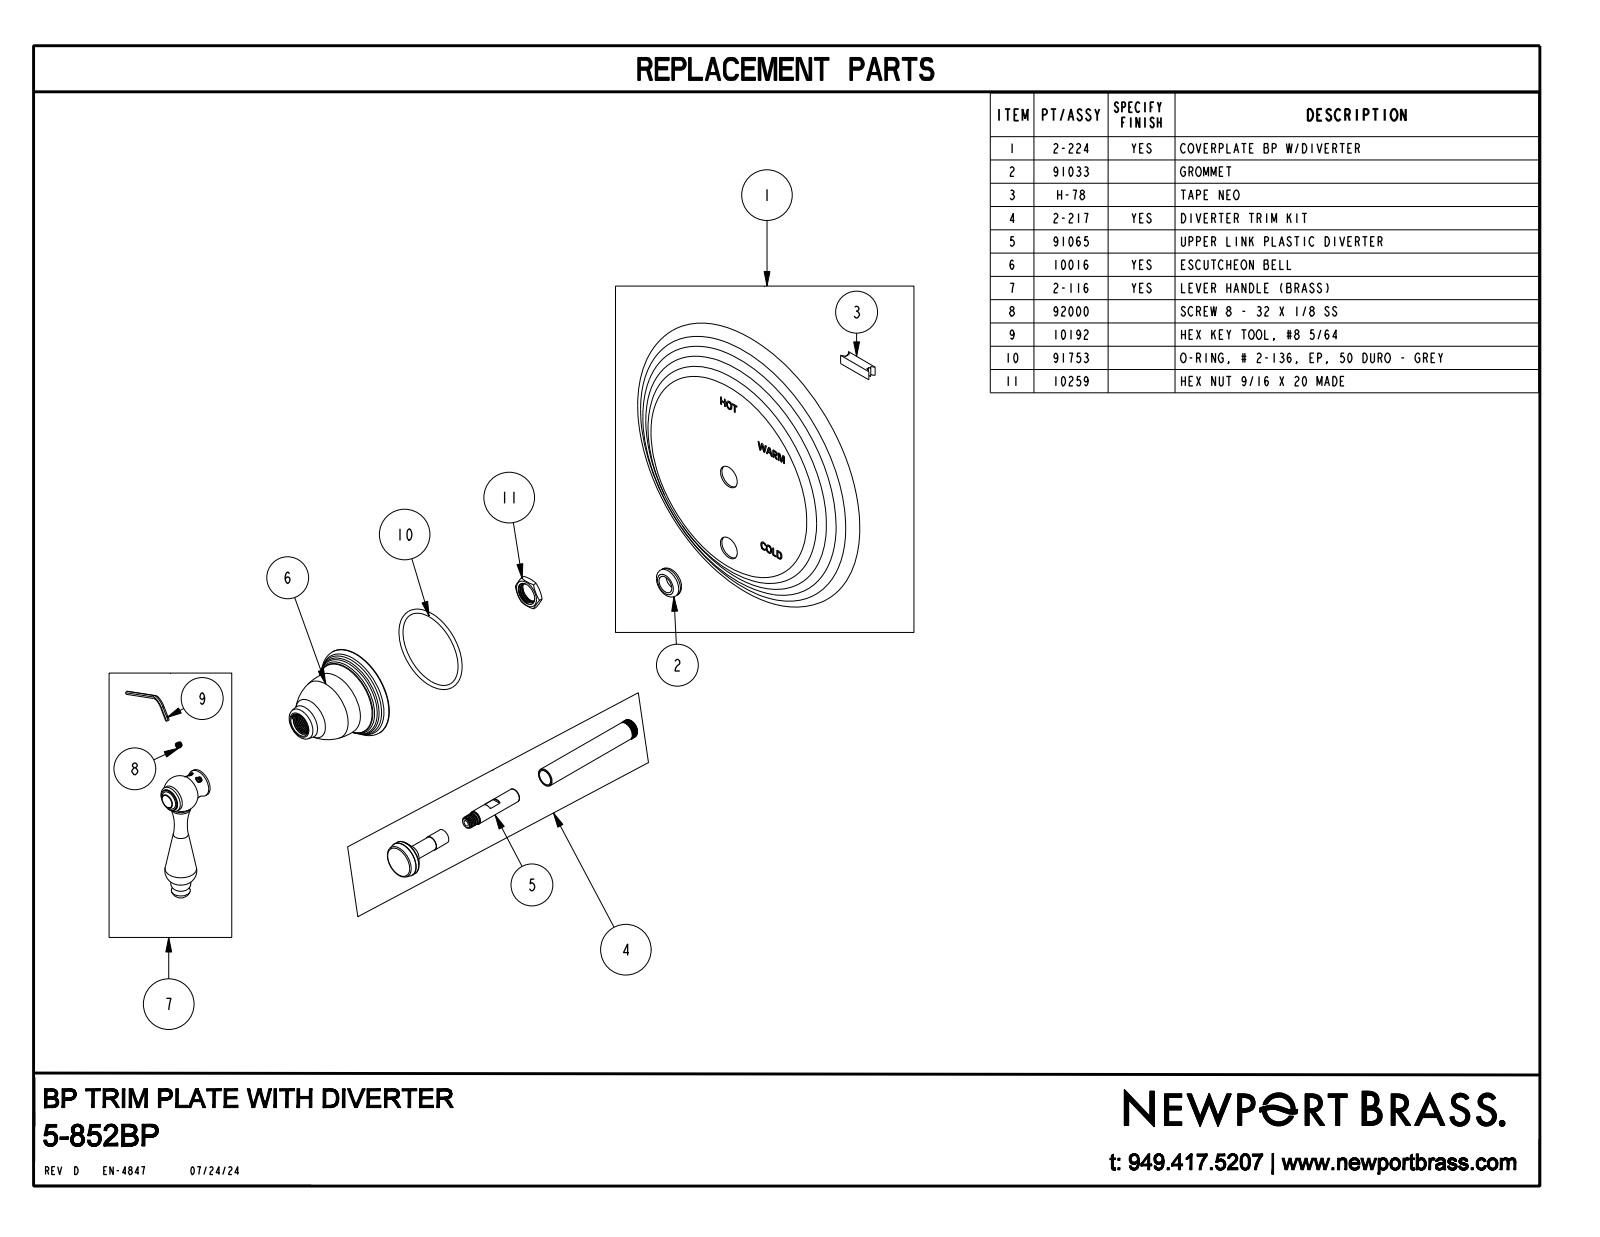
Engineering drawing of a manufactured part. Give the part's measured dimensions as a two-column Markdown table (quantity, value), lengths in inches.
| quantity | value |
| --- | --- |
| part name | 5-852BP |
| STEP written by | CREO PARAMETRIC BY PTC INC, 2018400 (CONFIG_CONTROL_DESIGN) |
| units | inches |
| bodies | 1 solid, 266 faces (110 planar, 18 cylindrical, 138 other) |
| overall size | 7.75 × 7.75 × 3.963 |
| volume | 33.01 in³ |
| surface area | 119.1 in² |
| round bosses / shafts (diameter × count) | 2.34 × 1, 0.9 × 1, 0.705 × 1, 0.661 × 1, 0.544 × 1, 0.5 × 1, 0.472 × 1, 0.4 × 1 |
| main face-to-face distances | 0.754, 2.106, 1.352, 2.793, 2.039, 0.687, 2.762, 2.008, 0.656, 0.031 |
